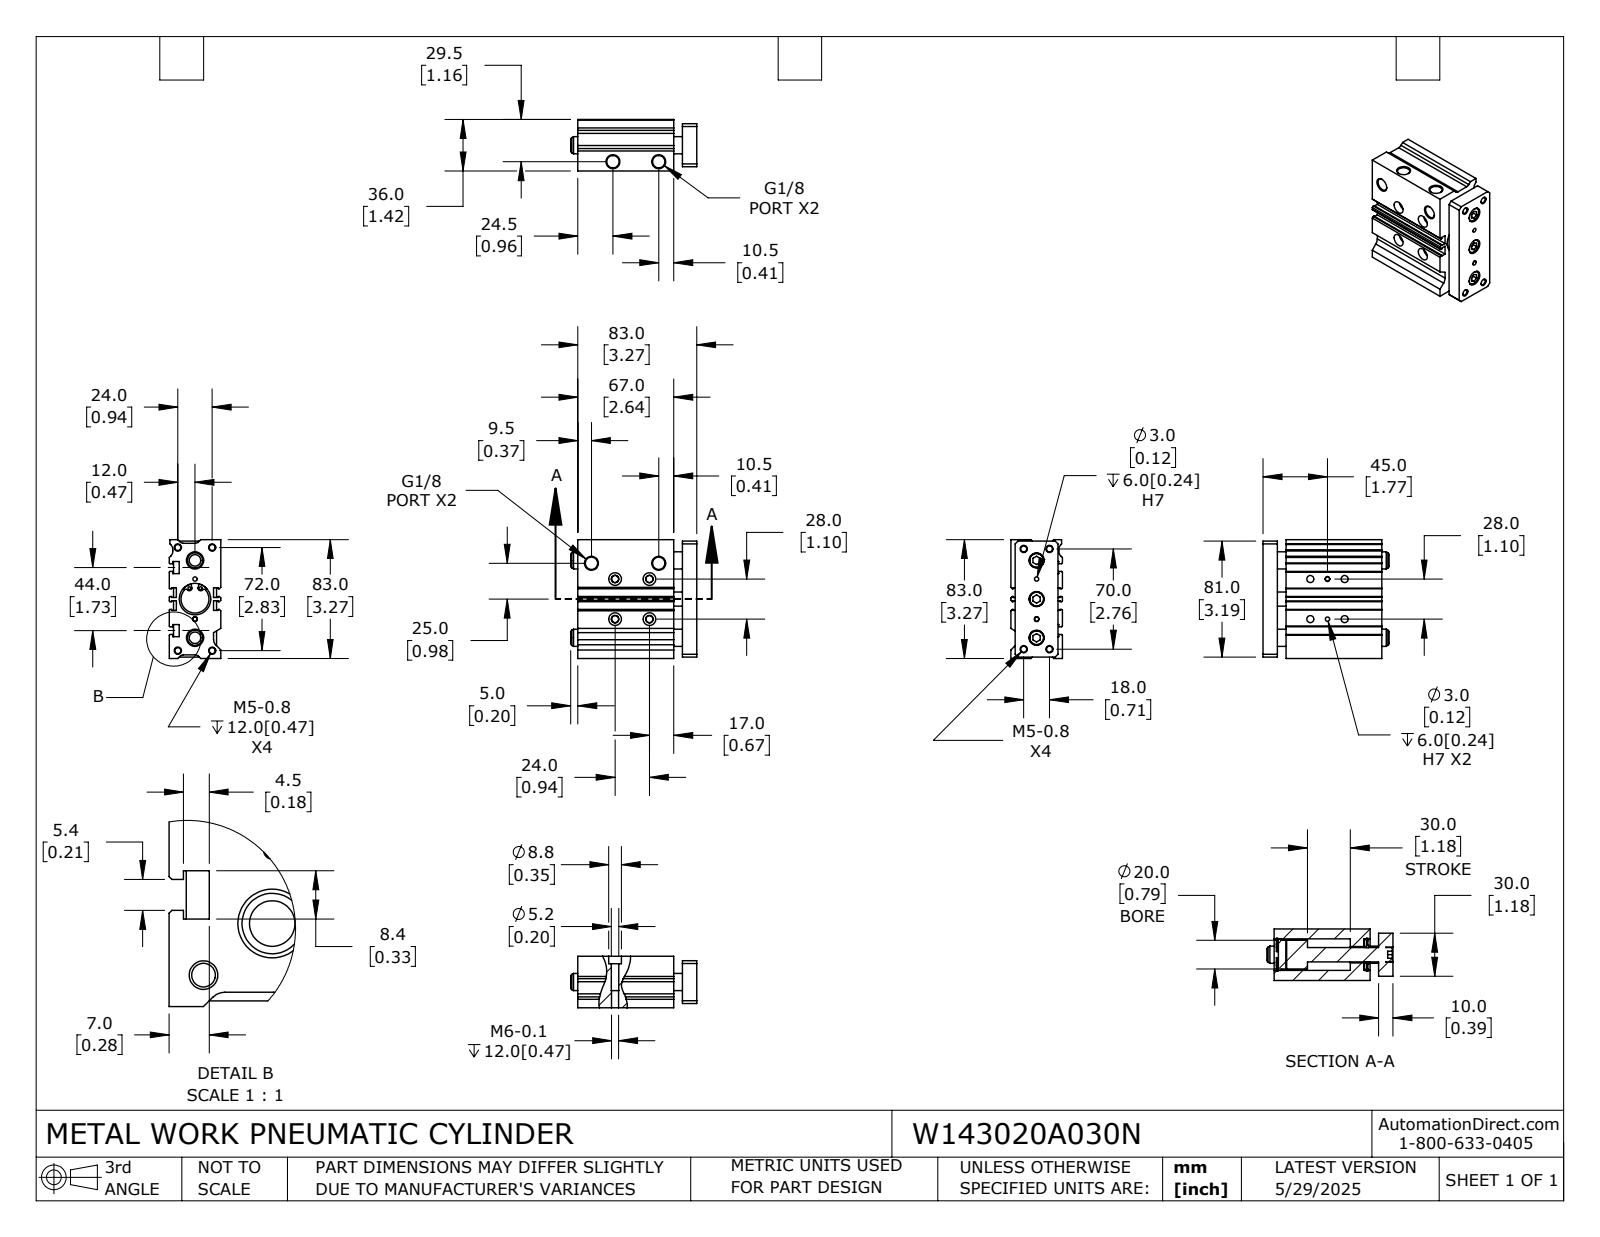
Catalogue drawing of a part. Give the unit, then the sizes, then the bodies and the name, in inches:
Units: inches
Overall size (bounding box): 3.465 × 3.268 × 1.417
Round holes (diameter × count): ⌀0.163 ×8, ⌀0.079 ×4, ⌀0.118 ×4, ⌀0.205 ×4, ⌀0.337 ×4, ⌀0.346 ×4, ⌀0.413 ×3, ⌀0.194 ×2, ⌀0.194 ×2, ⌀0.472 ×2, ⌀0.449 ×1, ⌀0.767 ×1
Round bosses / shafts (diameter × count): ⌀0.394 ×3, ⌀0.906 ×2, ⌀0.787 ×1, ⌀0.512 ×1
Partial cylindrical surfaces — rounded edges, fillets, slot ends (radius × count): R0.053 ×4, R0.059 ×4, R0.071 ×4, R0.118 ×4, R0.197 ×3
Main face-to-face distances: 3.268, 1.417, 0.098, 0.079, 0.197, 1.22, 0.394, 0.236, 0.63, 0.118
Hole centre spacings: 0.124, 0.296, 0.336, 0.472, 0.474, 0.591, 0.78, 0.828
Volume: 11.17 in³ · Surface area: 93.8 in²
Bodies: 6 solids, 357 faces (174 planar, 145 cylindrical, 38 other)
Part name (STEP PRODUCT): W143020A030N; W143020A030N_BODY; W143020A030N_ROD
STEP written by: SolidWorks 2024 (CONFIG_CONTROL_DESIGN)
